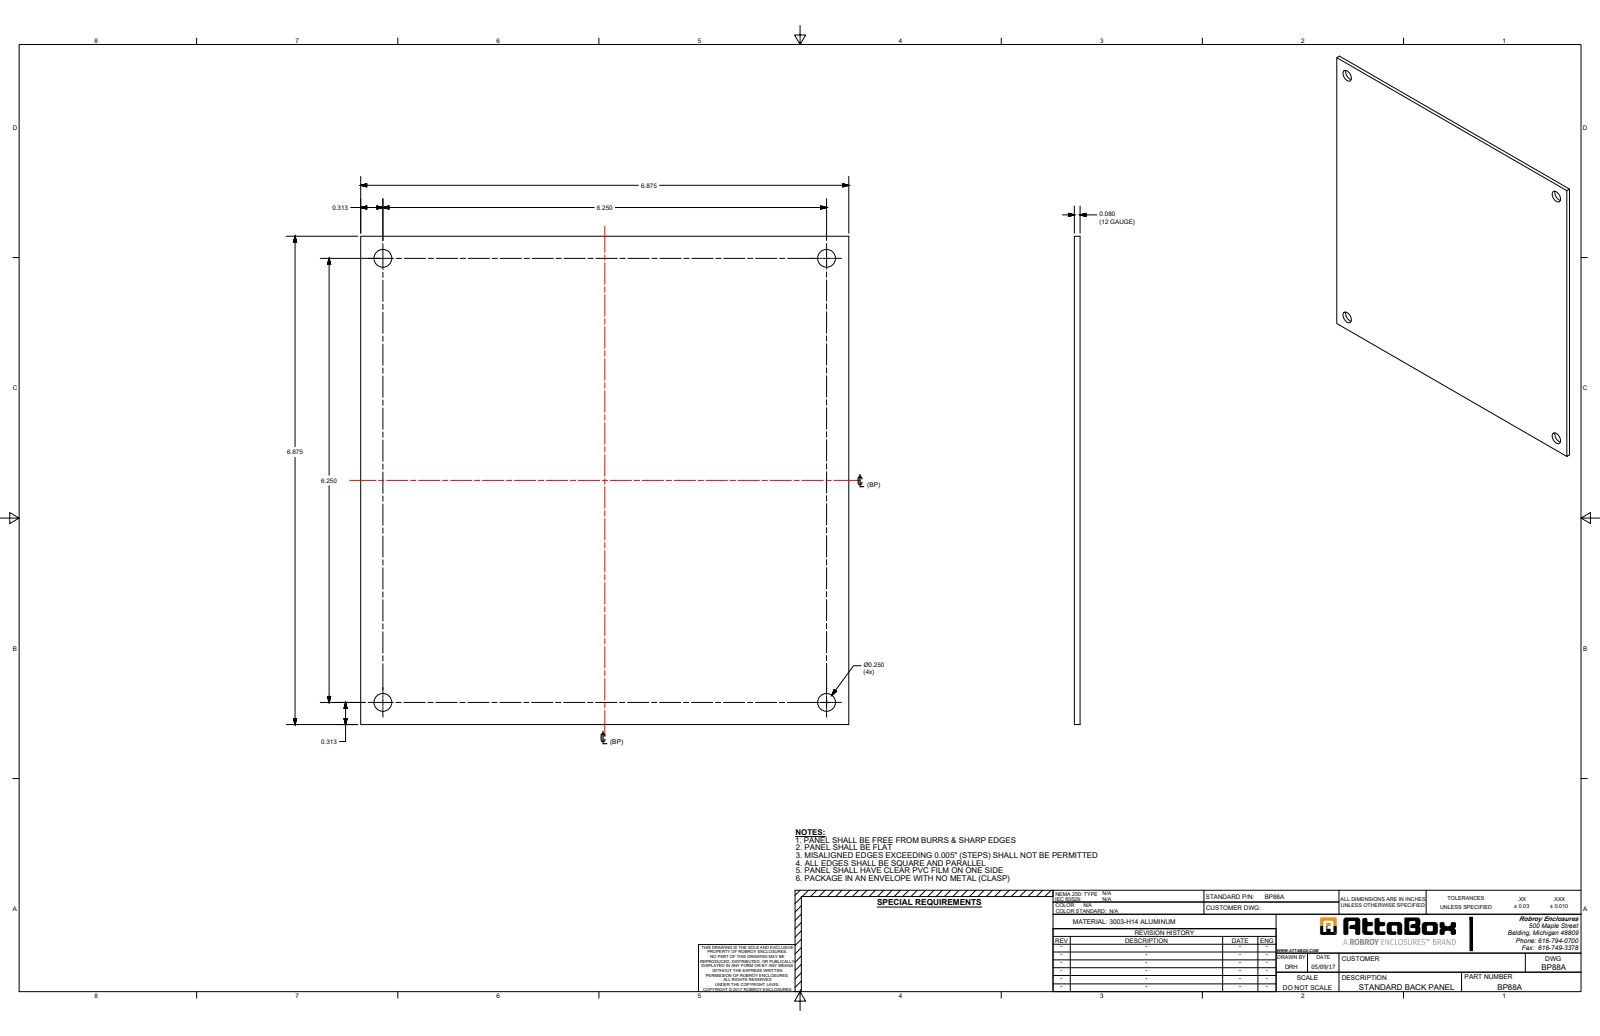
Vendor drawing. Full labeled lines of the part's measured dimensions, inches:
Part name (STEP PRODUCT): BP88A
STEP written by: SolidWorks 2023 (AUTOMOTIVE_DESIGN)
Units: inches
Bodies: 1 solid, 10 faces (6 planar, 4 cylindrical, 0 other)
Overall size (bounding box): 6.875 × 6.875 × 0.08
Volume: 3.766 in³ · Surface area: 96.59 in²
Round holes (diameter × count): ⌀0.25 ×4
Main face-to-face distances: 0.08, 6.875
Hole centre spacings: 6.25, 8.839
